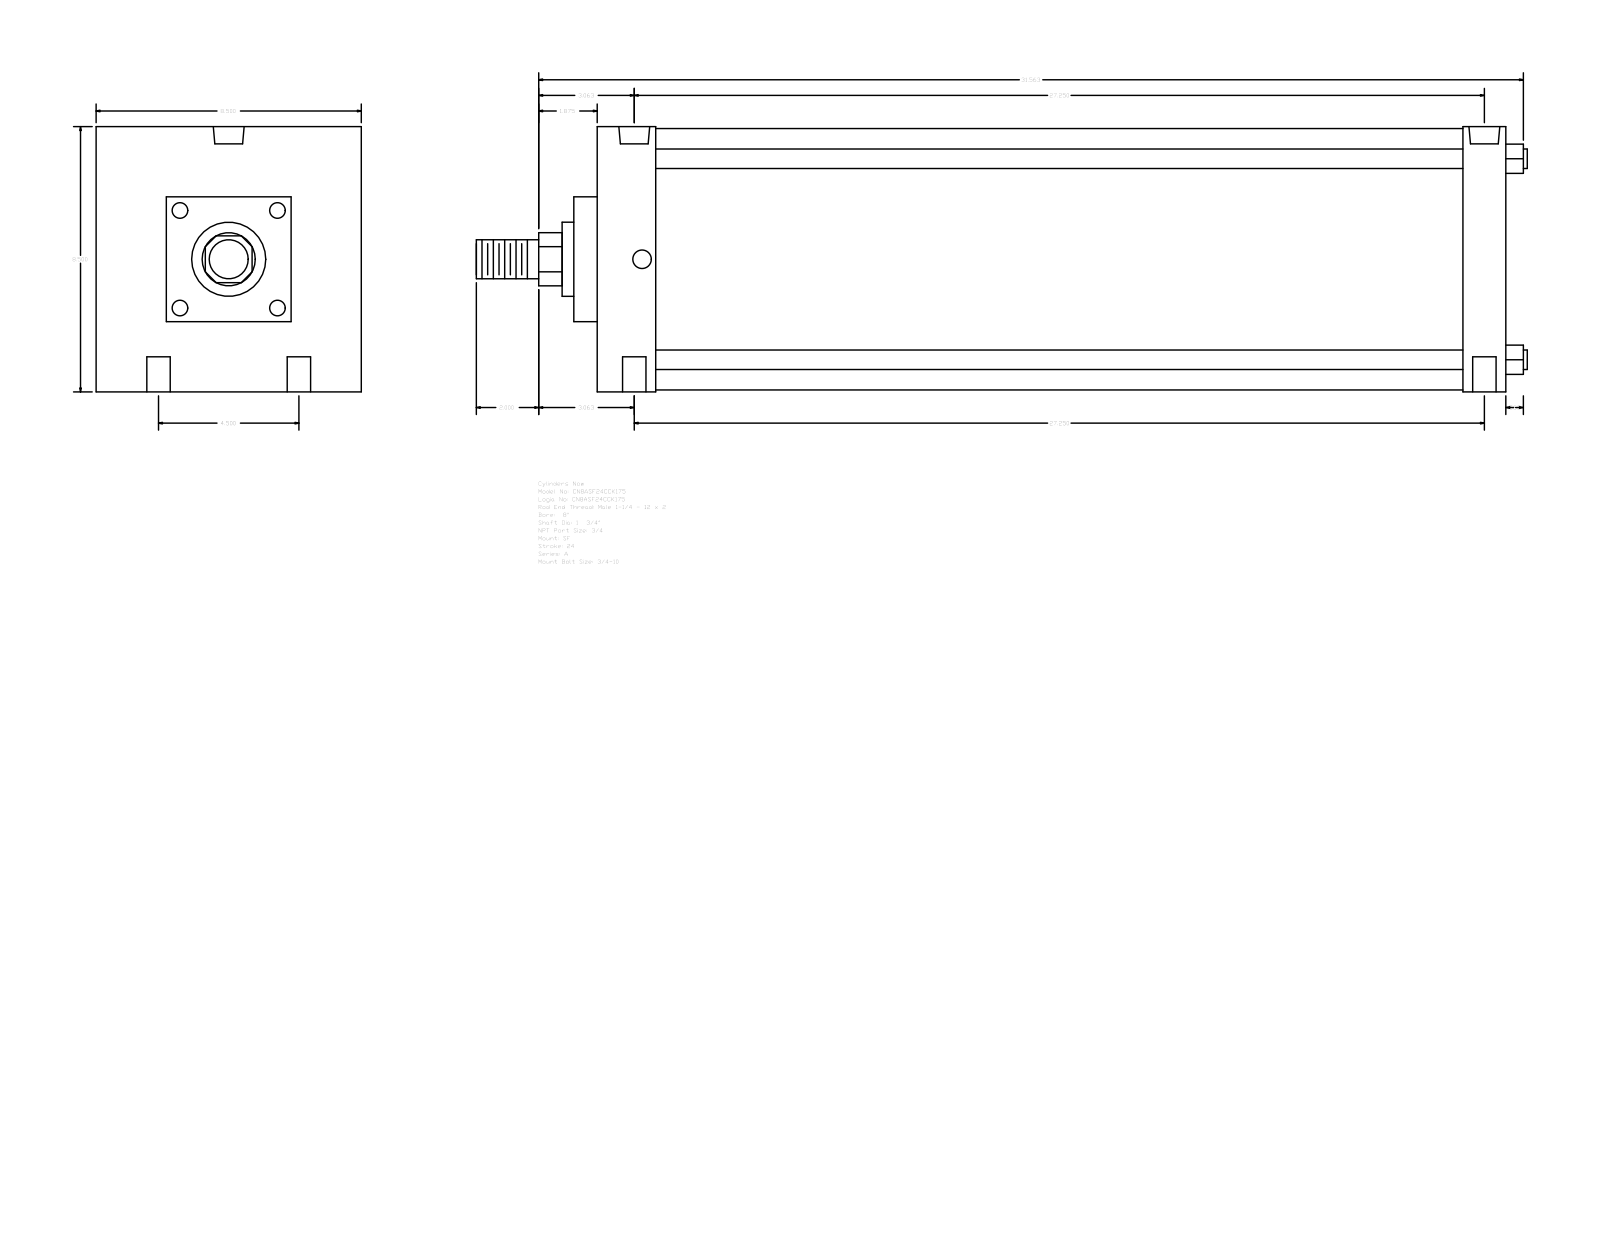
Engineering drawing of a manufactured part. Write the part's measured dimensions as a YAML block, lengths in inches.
part_name: "A_SF__0800_1.75"
step_written_by: "GSSL Pune (CONFIG_CONTROL_DESIGN)"
units: inches
bodies: {solids: 0, faces: 93, planar: 67, cylindrical: 26, other: 0}
overall_size: [33.687, 8.5, 8.5]
round_holes:
  - {diameter: 0.75, count: 4}
  - {diameter: 0.594, count: 2}
  - {diameter: 0.989, count: 2}
round_bosses_or_shafts:
  - {diameter: 0.625, count: 4}
  - {diameter: 8.375, count: 1}
  - {diameter: 2.375, count: 1}
  - {diameter: 1.75, count: 1}
  - {diameter: 1.25, count: 1}
partial_cylinders:
  - {radius: 0.852, count: 1}
face_to_face_distances: [29.125, 8.5, 1.875, 27.75, 25.875, 27.25, 1.375, 0.75, 6.25, 2.25]
hole_center_spacings: [2.25, 27.343, 27.25, 4.5, 27.619, 26.75]
